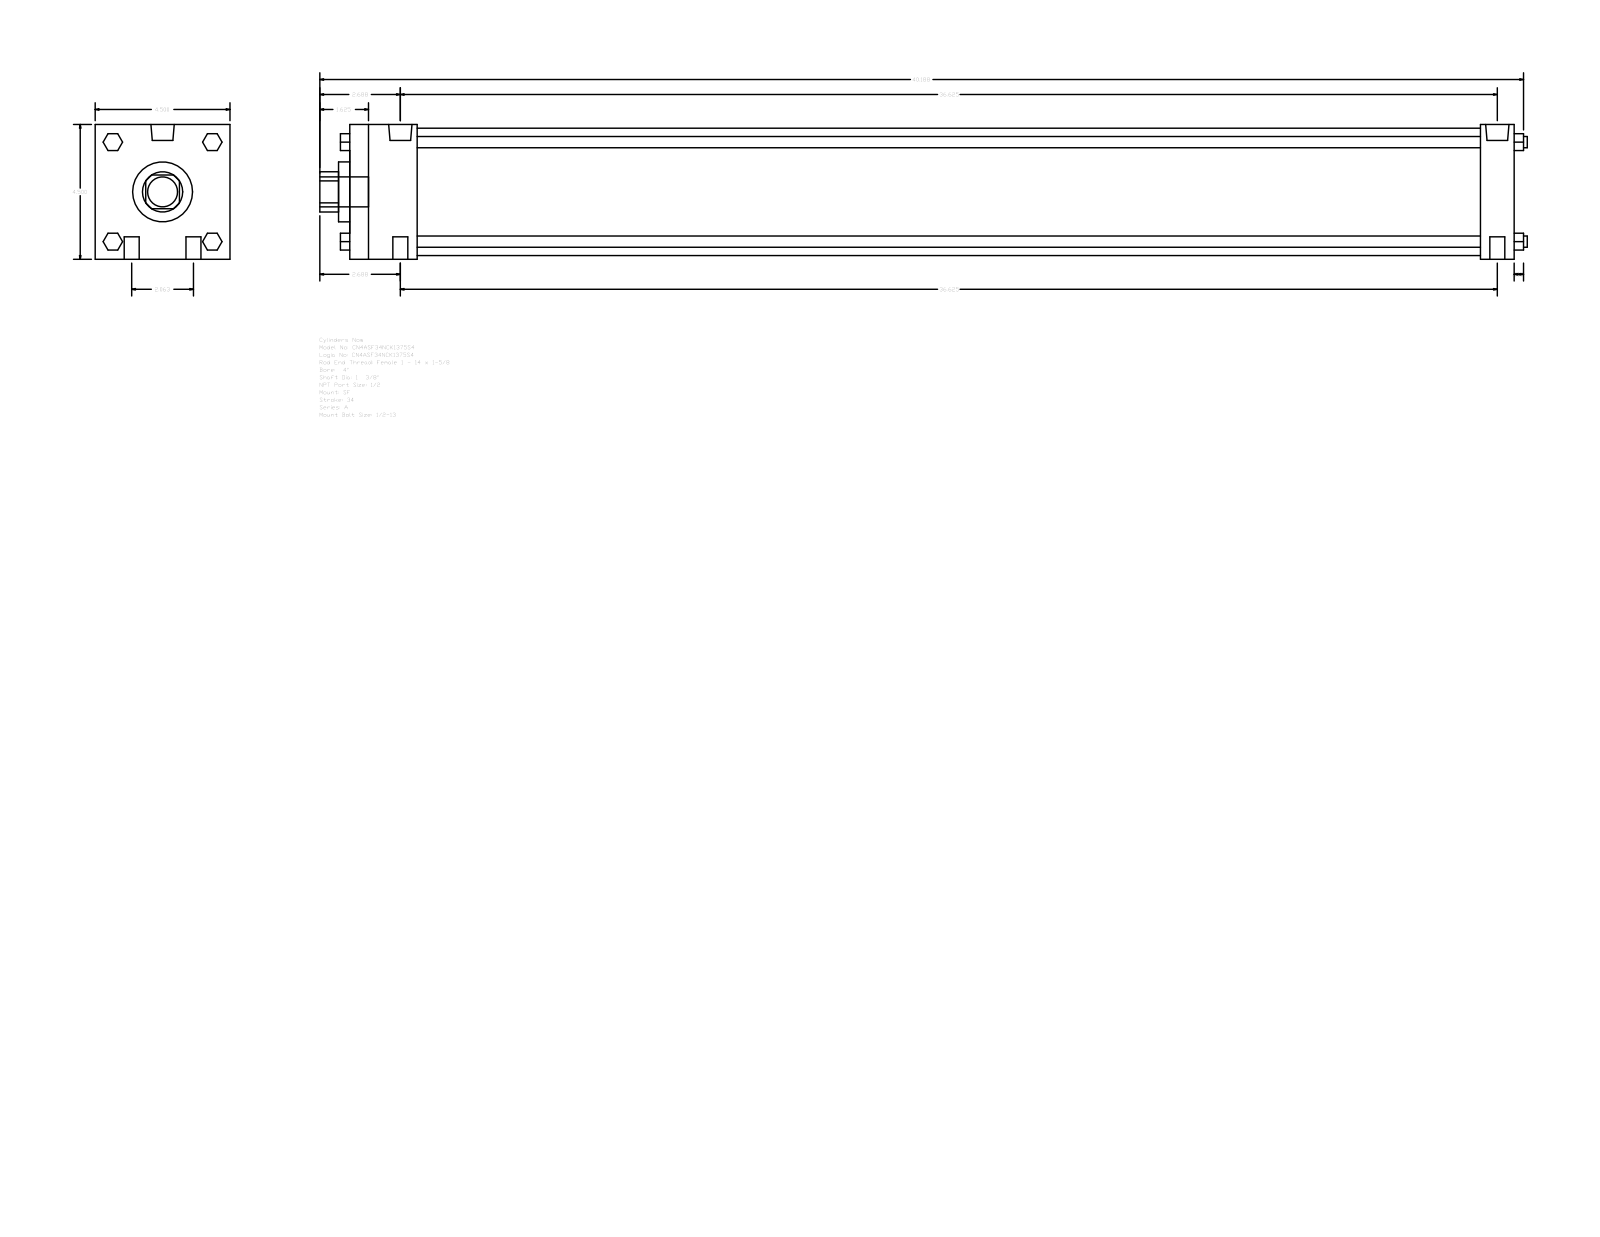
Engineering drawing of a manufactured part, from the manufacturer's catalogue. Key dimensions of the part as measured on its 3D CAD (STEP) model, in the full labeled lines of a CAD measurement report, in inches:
Part name (STEP PRODUCT): A_SF__0400_1.375
STEP written by: GSSL Pune (CONFIG_CONTROL_DESIGN)
Units: inches
Bodies: 0 solids, 124 faces (94 planar, 30 cylindrical, 0 other)
Overall size (bounding box): 40.313 × 4.5 × 4.5
Round holes (diameter × count): ⌀1.375 ×1, ⌀2 ×1, ⌀4.25 ×1
Round bosses / shafts (diameter × count): ⌀0.5 ×4, ⌀0.375 ×4, ⌀0.778 ×2, ⌀0.344 ×2, ⌀1 ×1
Partial cylindrical surfaces — rounded edges, fillets, slot ends (radius × count): R0.672 ×1
Main face-to-face distances: 4.5, 38.875, 1.125, 37.75, 2.25, 35.5, 36.625, 0.563, 0.375, 2.625
